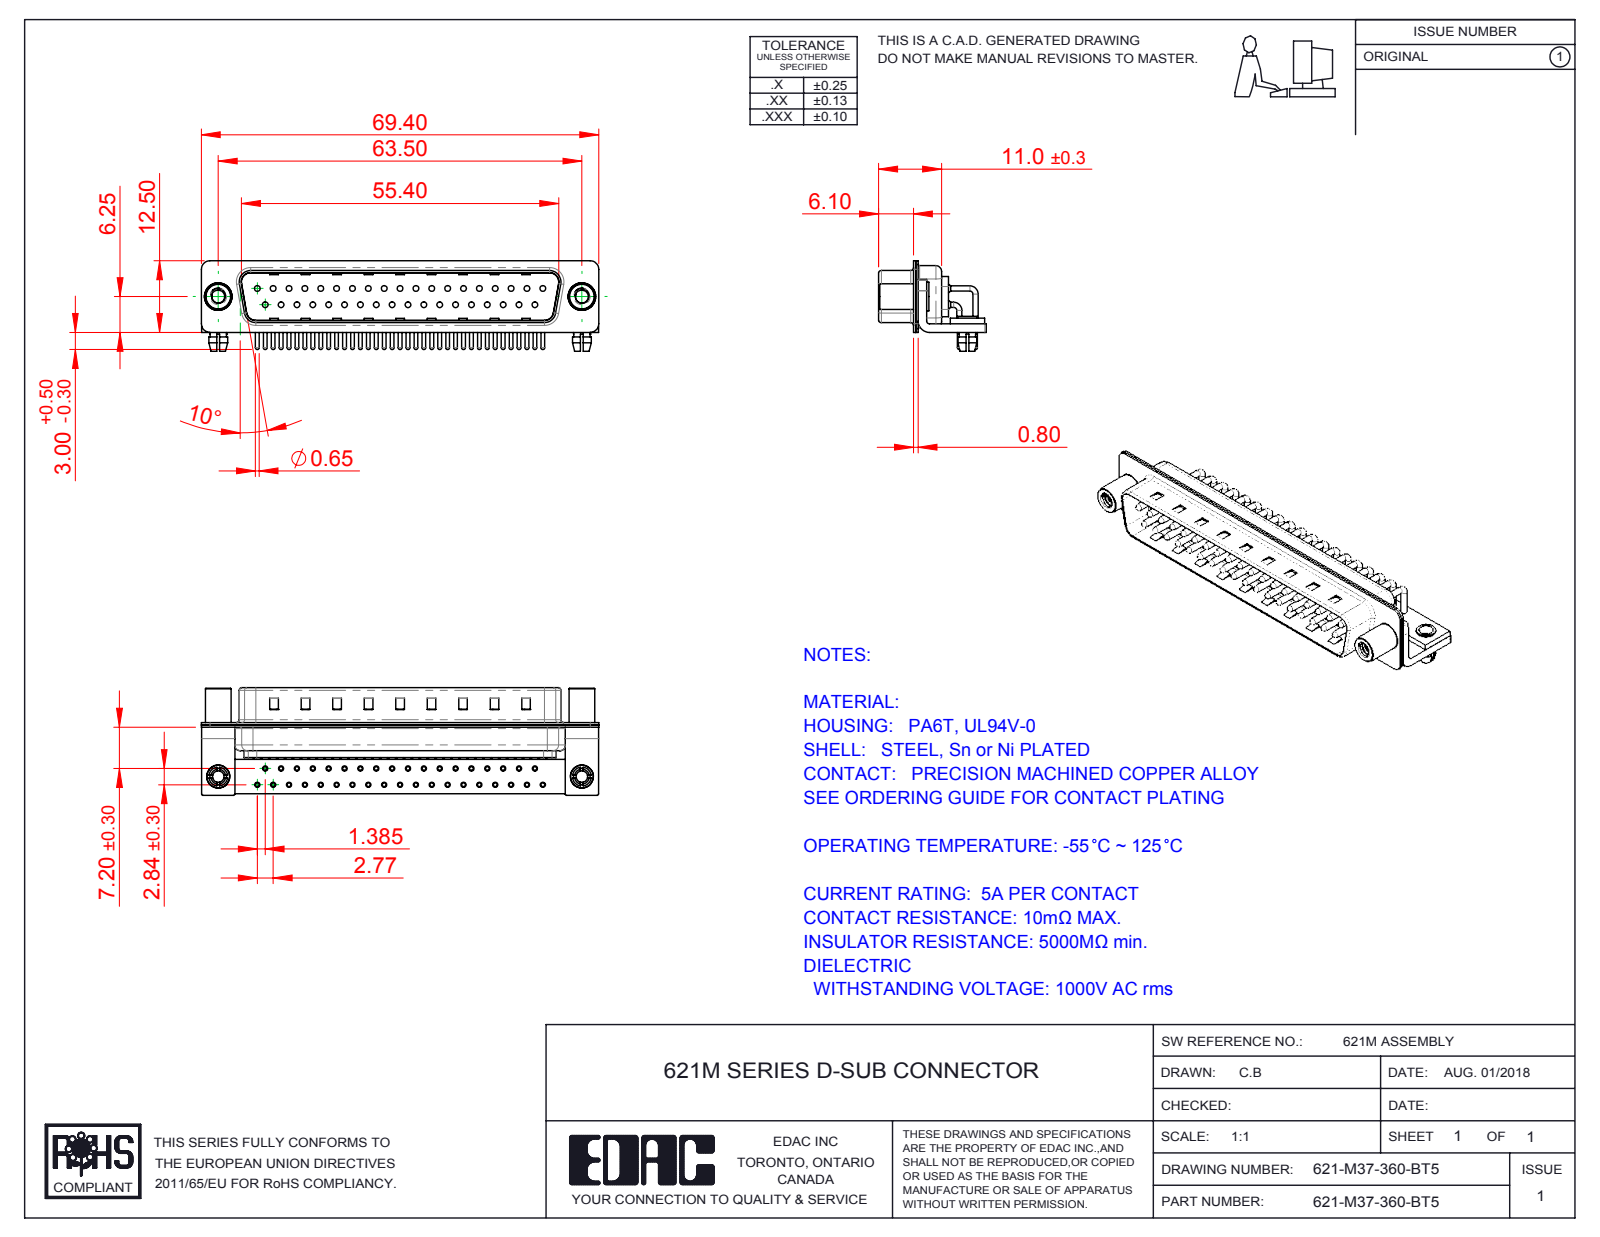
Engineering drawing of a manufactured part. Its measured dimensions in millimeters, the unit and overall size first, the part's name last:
Units: millimetres
Overall size (bounding box): 69.4 × 18.8 × 15.8
Round holes (diameter × count): ⌀2 ×39, ⌀0.9 ×37, ⌀1 ×37, ⌀1.7 ×37, ⌀2.26 ×2, ⌀2.5 ×2, ⌀3.2 ×2, ⌀4 ×2, ⌀4.8 ×2
Round bosses / shafts (diameter × count): ⌀0.9 ×46, ⌀1.5 ×37, ⌀0.65 ×37, ⌀5 ×2, ⌀4.9 ×2, ⌀4.5 ×2, ⌀4 ×2, ⌀3.4 ×2
Partial cylindrical surfaces — rounded edges, fillets, slot ends (radius × count): R1.01 ×37, R0.25 ×16, R1.5 ×16, R2 ×13, R0.5 ×9, R1.6 ×8, R0.6 ×4, R0.65 ×4
Main face-to-face distances: 0.4, 0.85, 1.25, 9.55, 1.5, 10.4, 8.3, 0.8, 8.7, 1
Hole centre spacings: 3.16, 2.77, 5.54, 8.31, 11.08, 13.85, 5.03, 16.62
Volume: 4 770 mm³ · Surface area: 12 476 mm²
Bodies: 47 solids, 4748 faces (2647 planar, 1643 cylindrical, 458 other)
Part name (STEP PRODUCT): 621-M37-360-BT5; 621M Stabilizer Bracket; 621M Stabilizer Board_37 Contacts; 621M Contact Row 1 (+6 more)
STEP written by: SolidWorks 2016 (CONFIG_CONTROL_DESIGN)
